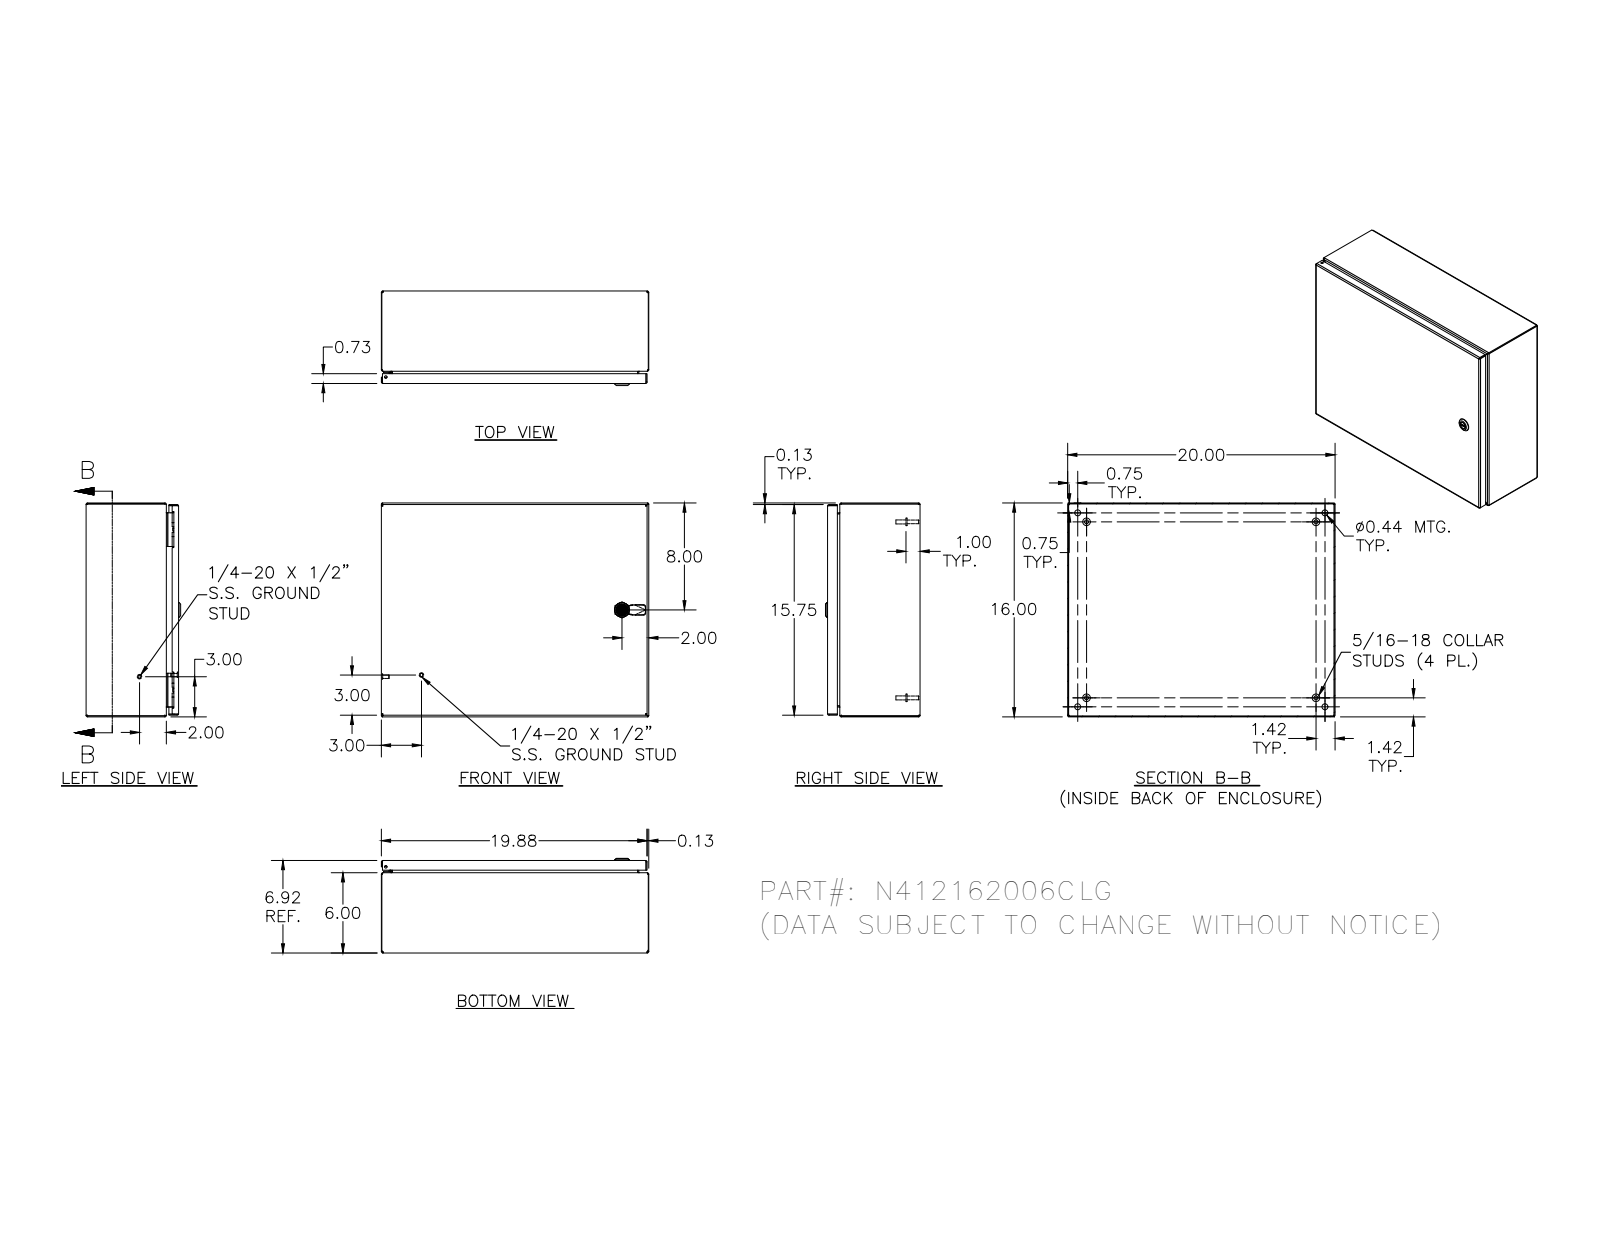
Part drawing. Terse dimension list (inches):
name: N412162006CLG
written by: SolidWorks 2018 (AUTOMOTIVE_DESIGN)
unit: in
bodies: 33 solids, 1449 faces (530 planar, 547 cylindrical, 372 other)
size: 20 × 16 × 7.075
volume: 90.42 in³; area: 2 461 in²
holes: 5× ⌀0.188, 4× ⌀0.093, 4× ⌀0.152, 4× ⌀0.167, 4× ⌀0.172, 4× ⌀0.437, 2× ⌀0.156, 1× ⌀0.187, 1× ⌀0.197, 1× ⌀0.315, 1× ⌀0.394, 1× ⌀0.402
bosses: 10× ⌀0.25, 4× ⌀0.563, 4× ⌀0.36, 4× ⌀0.32, 4× ⌀0.3, 4× ⌀0.275, 4× ⌀0.256, 4× ⌀0.164
rounds: 30× R0.012, 30× R0.031, 26× R0.05, 20× R0.105, 18× R0.016, 16× R0.125, 13× R0.02, 8× R0.032
face distances: 0.074, 6.843, 6.769, 6.917, 0.074, 15.852, 15.926, 15.926, 16, 19.926
hole spacings: 12, 0.66, 0.656, 1.307, 1.965, 11.34, 11.996, 12.656
